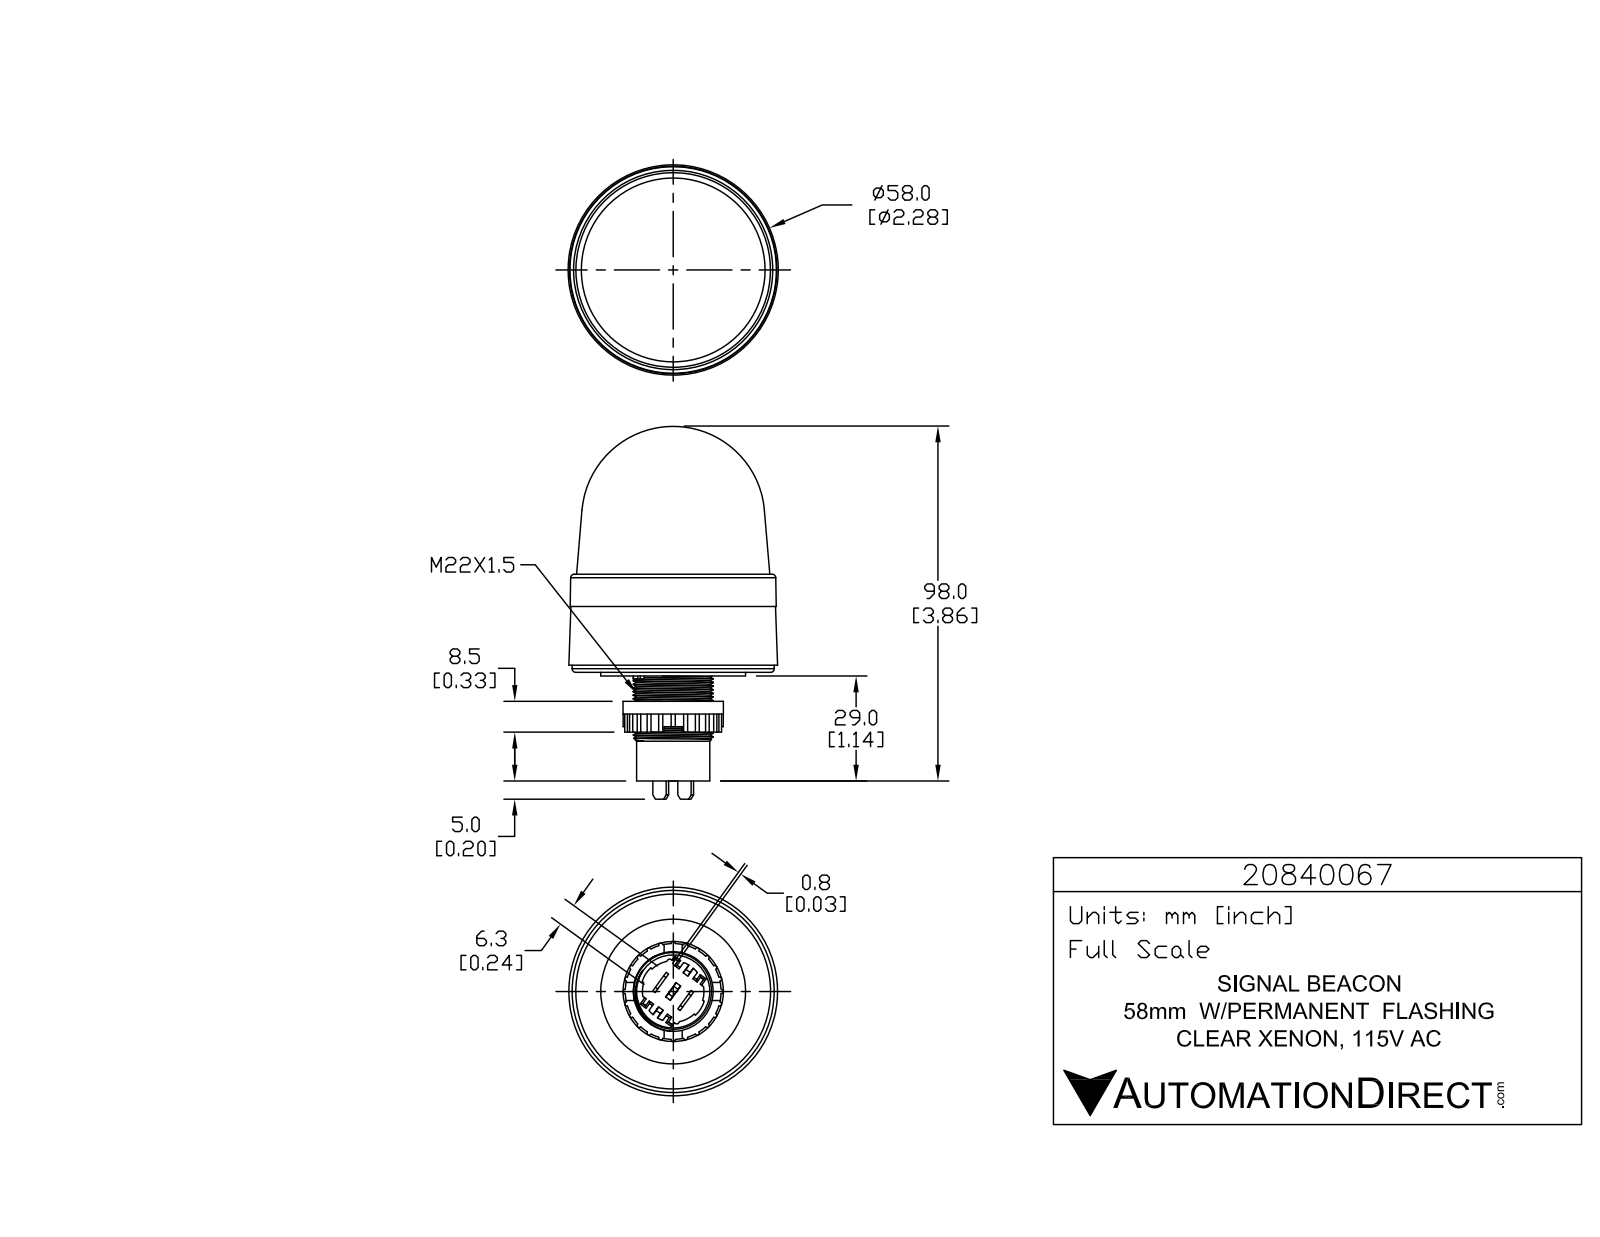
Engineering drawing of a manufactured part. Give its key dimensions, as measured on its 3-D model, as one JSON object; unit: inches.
{"part_name": "20840067", "step_written_by": "SolidWorks 2015 (AUTOMOTIVE_DESIGN)", "units": "inches", "bodies": {"solids": 1, "faces": 266, "planar": 119, "cylindrical": 120, "other": 27}, "overall_size": [4.051, 2.269, 2.269], "volume_in3": 9.016, "surface_area_in2": 31.05, "round_holes": [[0.906, 1]], "round_bosses_or_shafts": [[2.197, 1], [1.575, 1], [1.091, 1], [0.866, 1], [0.795, 1]], "partial_cylinders_radius": [[0.023, 24], [0.02, 2], [0.335, 1], [0.354, 1], [0.522, 1]], "face_to_face_distances": [0.039, 0.276, 0.118, 1.142, 0.335, 0.315, 1.063, 0.748, 1.024, 0.728]}
